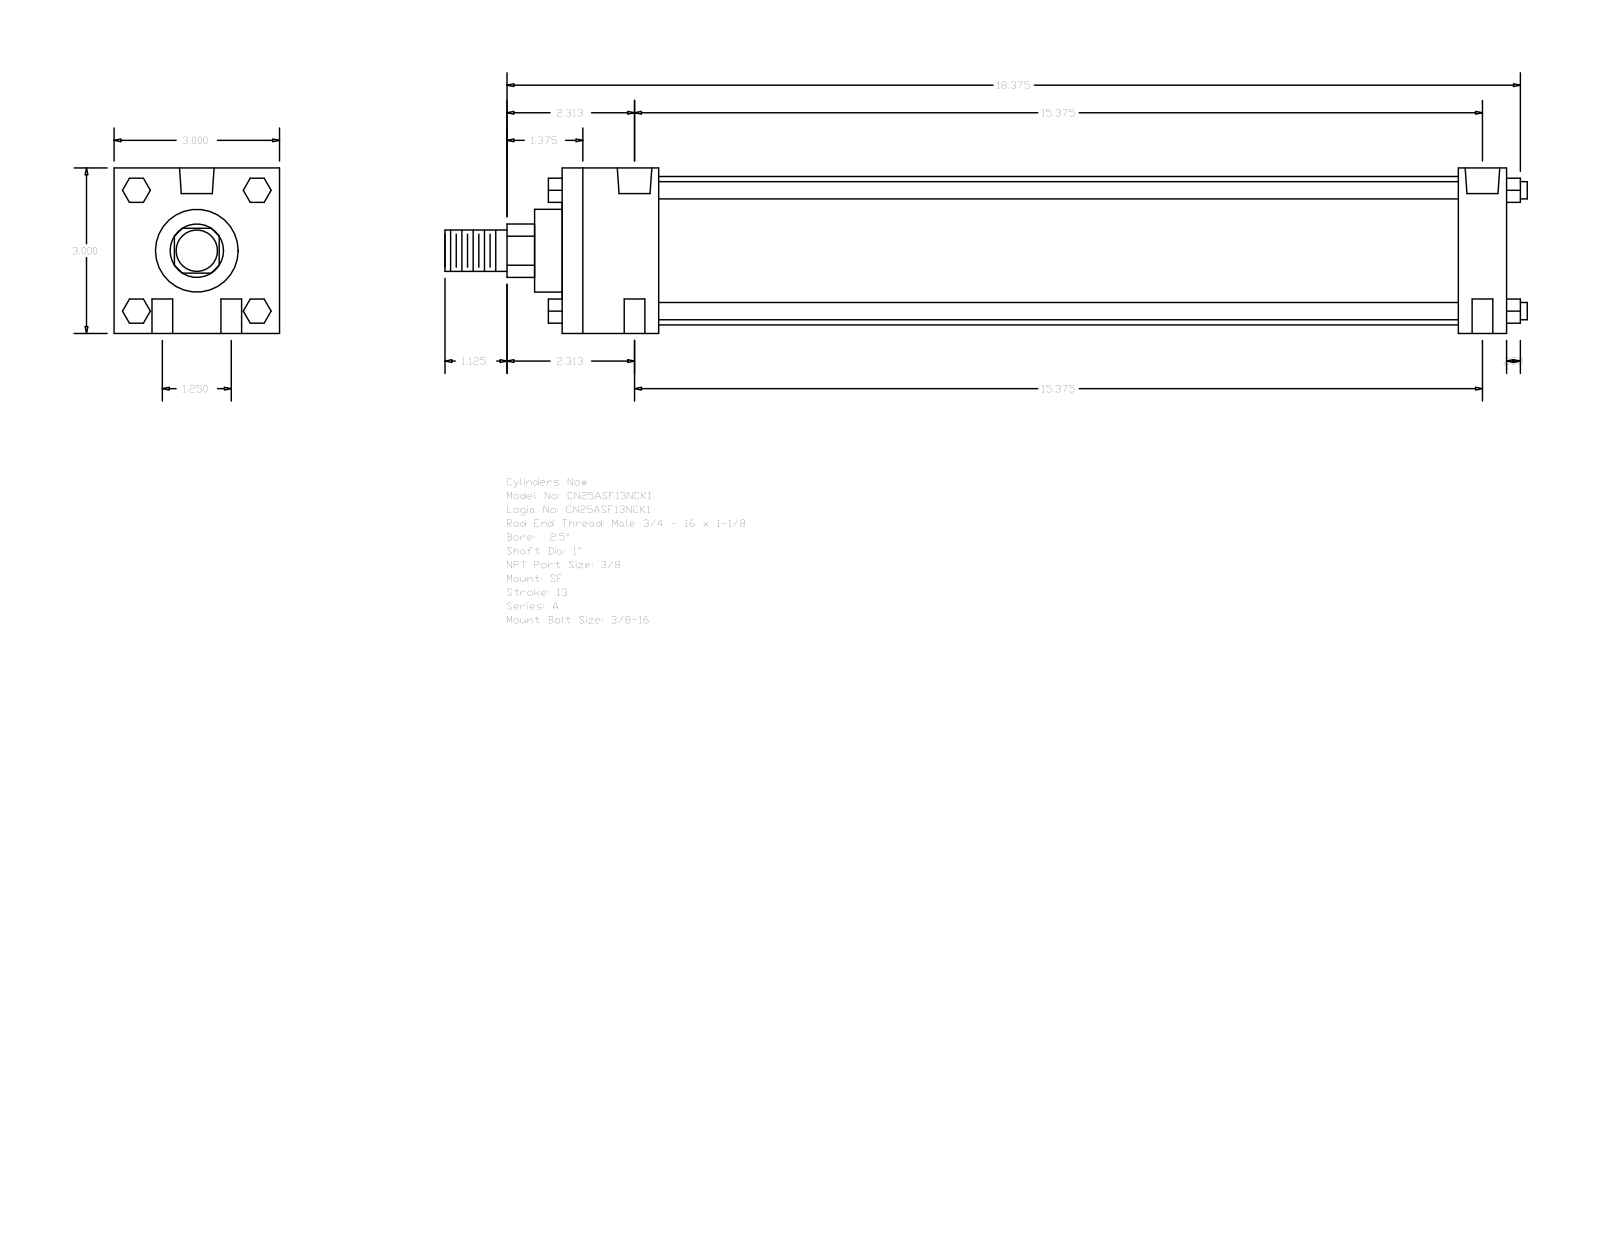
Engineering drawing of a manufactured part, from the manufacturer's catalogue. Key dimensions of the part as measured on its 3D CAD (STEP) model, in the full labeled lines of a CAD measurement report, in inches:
Part name (STEP PRODUCT): A_SF__0250_1
STEP written by: GSSL Pune (CONFIG_CONTROL_DESIGN)
Units: inches
Bodies: 0 solids, 124 faces (94 planar, 30 cylindrical, 0 other)
Overall size (bounding box): 19.625 × 3 × 3
Round holes (diameter × count): ⌀0.375 ×4, ⌀0.219 ×2, ⌀0.627 ×2
Round bosses / shafts (diameter × count): ⌀0.313 ×4, ⌀2.69 ×1, ⌀1.5 ×1, ⌀1 ×1, ⌀0.75 ×1
Partial cylindrical surfaces — rounded edges, fillets, slot ends (radius × count): R0.484 ×1
Main face-to-face distances: 3, 17.125, 16.25, 0.875, 1.75, 14.5, 15.375, 0.5, 17.625, 0.25
Hole centre spacings: 0.625, 15.387, 15.375, 1.25, 15.426, 15.562
